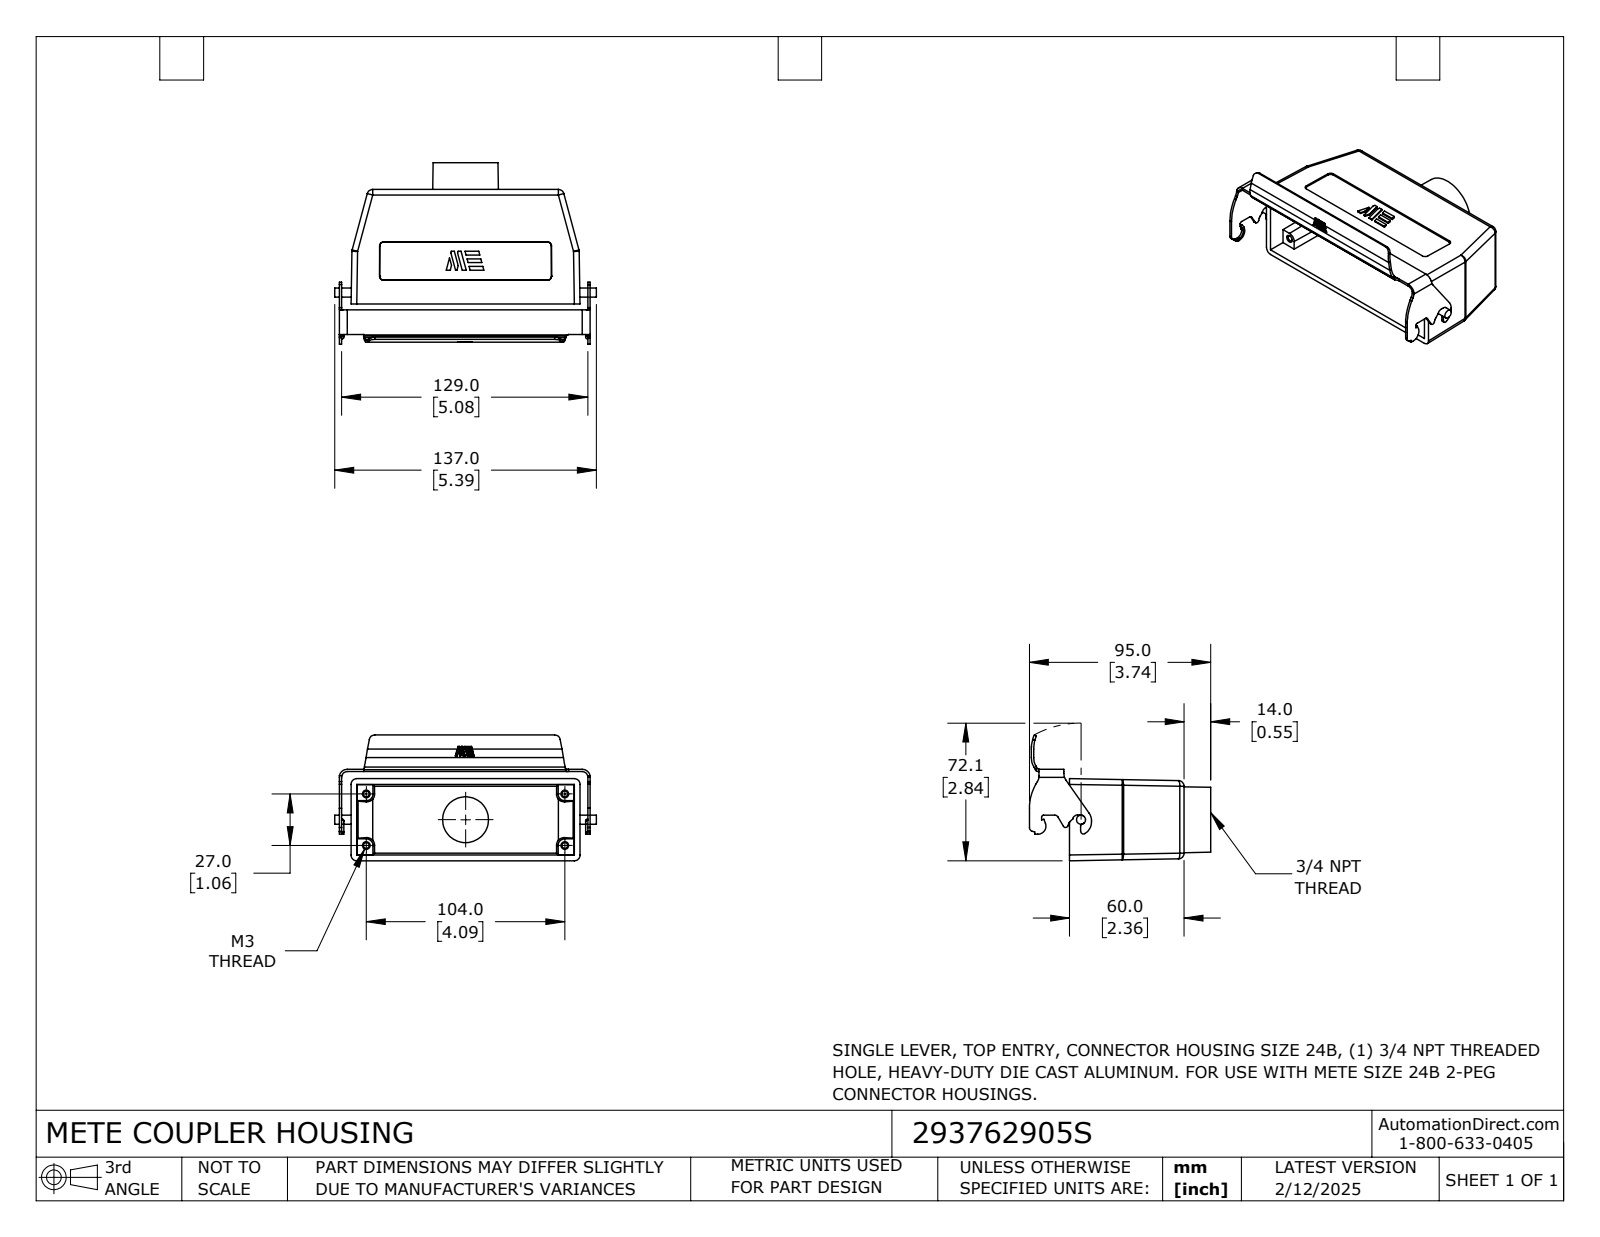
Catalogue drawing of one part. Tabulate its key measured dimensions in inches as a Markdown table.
| quantity | value |
| --- | --- |
| part name | 293762905S |
| STEP written by | SolidWorks 2024 (CONFIG_CONTROL_DESIGN) |
| units | inches |
| bodies | 1 solid, 318 faces (173 planar, 119 cylindrical, 26 other) |
| overall size | 5.394 × 3.74 × 2.594 |
| volume | 4.853 in³ |
| surface area | 88.81 in² |
| round holes (diameter × count) | 0.118 × 4, 0.945 × 1, 1.063 × 1 |
| round bosses / shafts (diameter × count) | 0.185 × 1 |
| partial cylindrical surfaces (radius × count) | 0.118 × 19, 0.008 × 17, 0.079 × 11, 0.039 × 6, 0.098 × 3, 0.165 × 3, 0.059 × 2, 0.114 × 2 |
| main face-to-face distances | 0.118, 0.047, 0.031, 0.087, 0.447, 0.329, 5.126, 2.362, 2.244, 5.079 |
| hole center spacings | 2.115, 1.063, 4.094, 4.23 |
